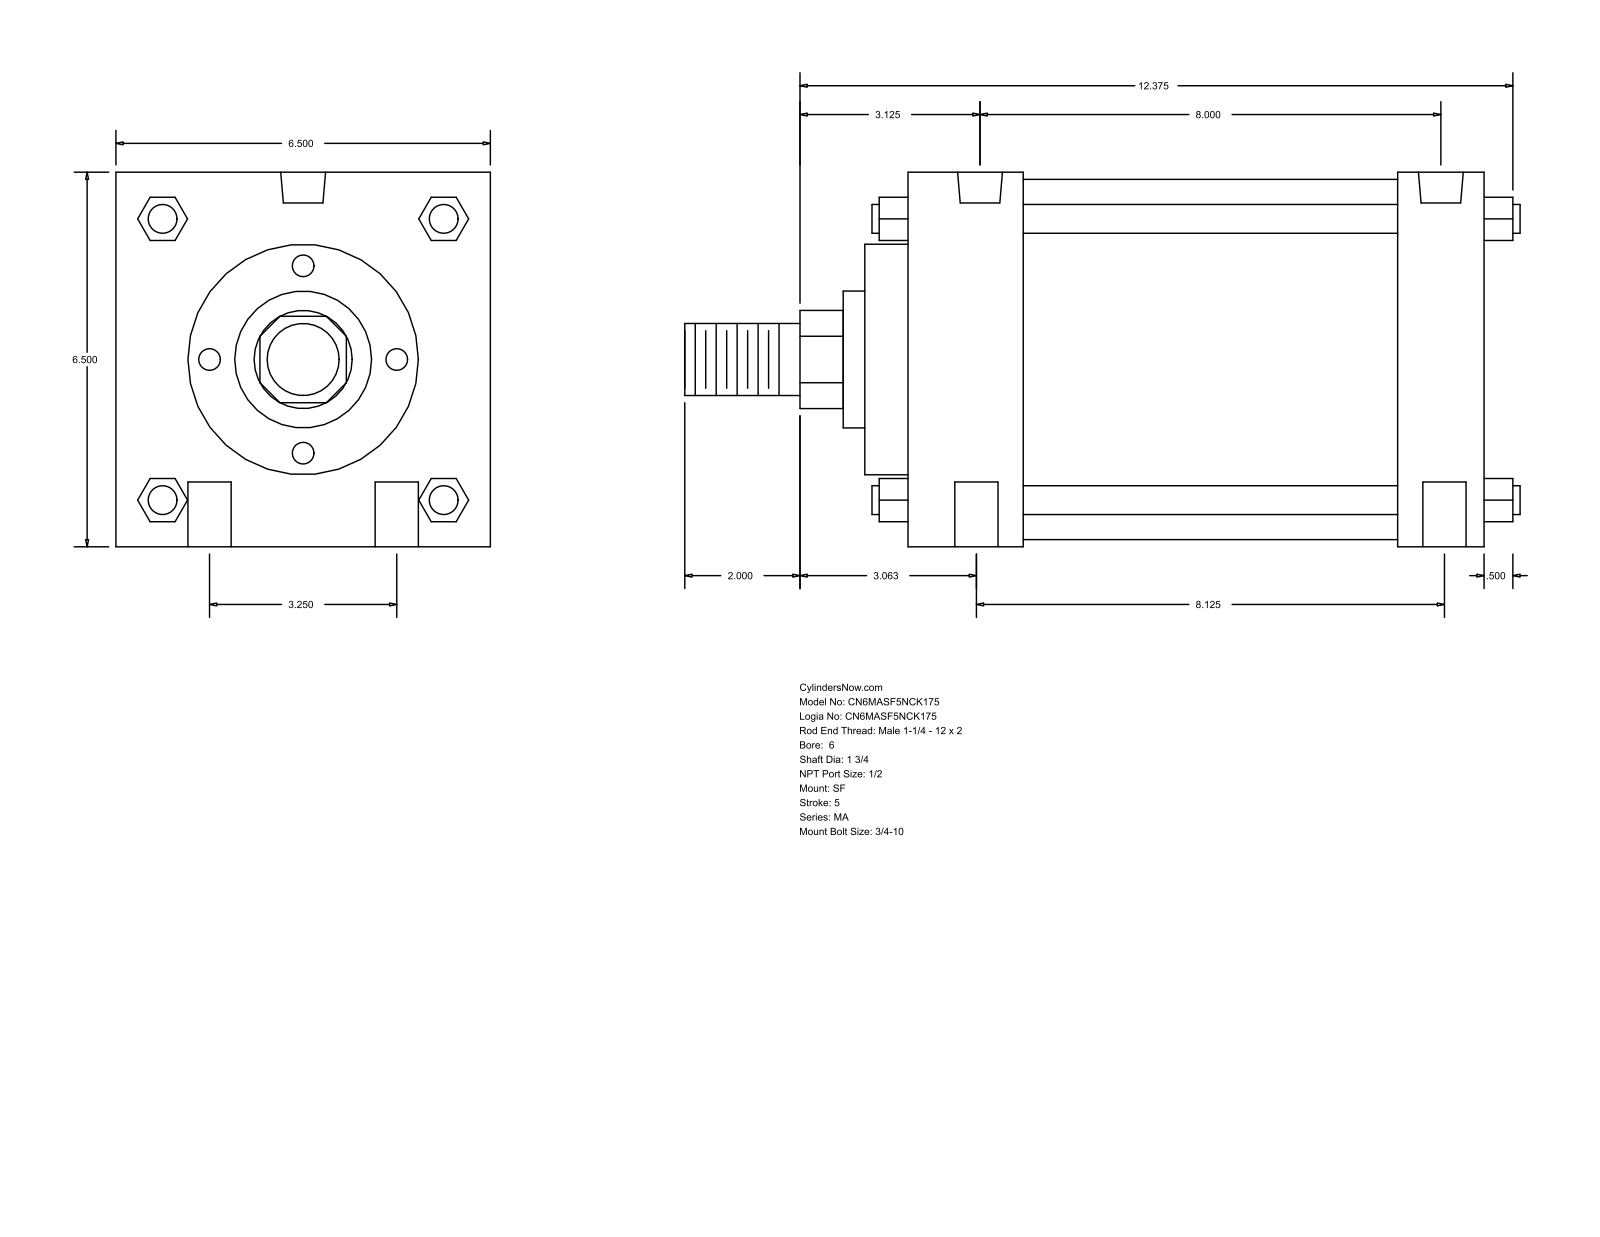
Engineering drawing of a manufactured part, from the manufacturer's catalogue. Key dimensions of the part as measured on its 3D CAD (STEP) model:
Part name (STEP PRODUCT): MA_SF__0600_1.75
STEP written by: GSSL Pune (CONFIG_CONTROL_DESIGN)
Units: millimetres
Bodies: 0 solids, 126 faces (95 planar, 31 cylindrical, 0 other)
Overall size (bounding box): 368.3 × 165.1 × 165.1
Round holes (diameter × count): ⌀19.05 ×4, ⌀17.46 ×2, ⌀19.77 ×2
Round bosses / shafts (diameter × count): ⌀12.7 ×4, ⌀158.75 ×1, ⌀101.6 ×1, ⌀60.33 ×1, ⌀44.45 ×1, ⌀31.75 ×1
Partial cylindrical surfaces — rounded edges, fillets, slot ends (radius × count): R21.63 ×1
Main face-to-face distances: 165.1, 254, 19.05, 50.8, 215.9, 38.1, 203.2, 69.85, 234.95, 273.05
Hole centre spacings: 41.3, 208.9, 82.54, 203.19, 206.37, 222.26
